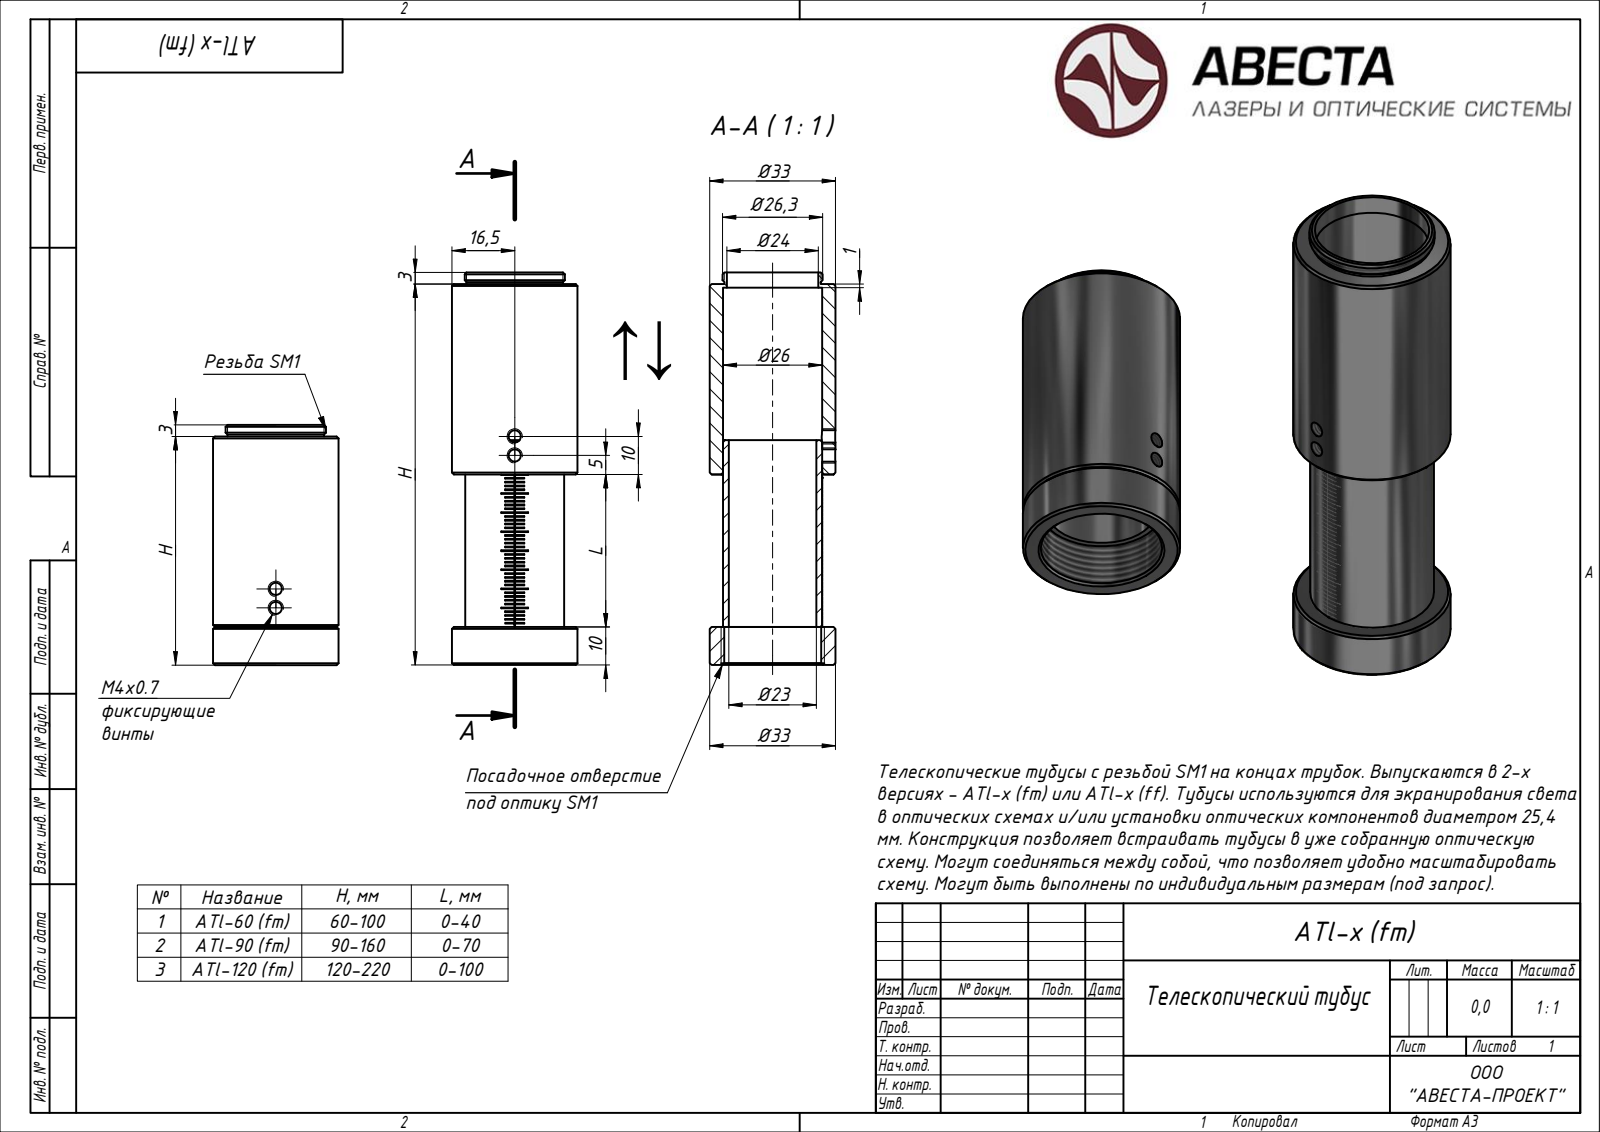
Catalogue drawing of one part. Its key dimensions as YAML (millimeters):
step_written_by: "Rhino 7.34 (AUTOMOTIVE_DESIGN)"
units: millimeters
bodies: {solids: 3, faces: 1893, planar: 1713, cylindrical: 108, other: 72}
overall_size: [223, 173, 33]
volume: 117021
surface_area: 90451
round_holes:
  - {diameter: 3.24, count: 6}
  - {diameter: 23, count: 3}
  - {diameter: 23.26, count: 3}
  - {diameter: 24, count: 3}
round_bosses_or_shafts:
  - {diameter: 33, count: 3}
  - {diameter: 26.29, count: 3}
  - {diameter: 26, count: 3}
  - {diameter: 25.29, count: 3}
partial_cylinders:
  - {radius: 13, count: 3}
  - {radius: 13.5, count: 3}
face_to_face_distances: [60, 10, 50, 110, 100, 30, 80, 120, 40, 160]
hole_center_spacings: [76.16, 5, 70, 74.33, 78.26, 152.32, 140, 150.42]
